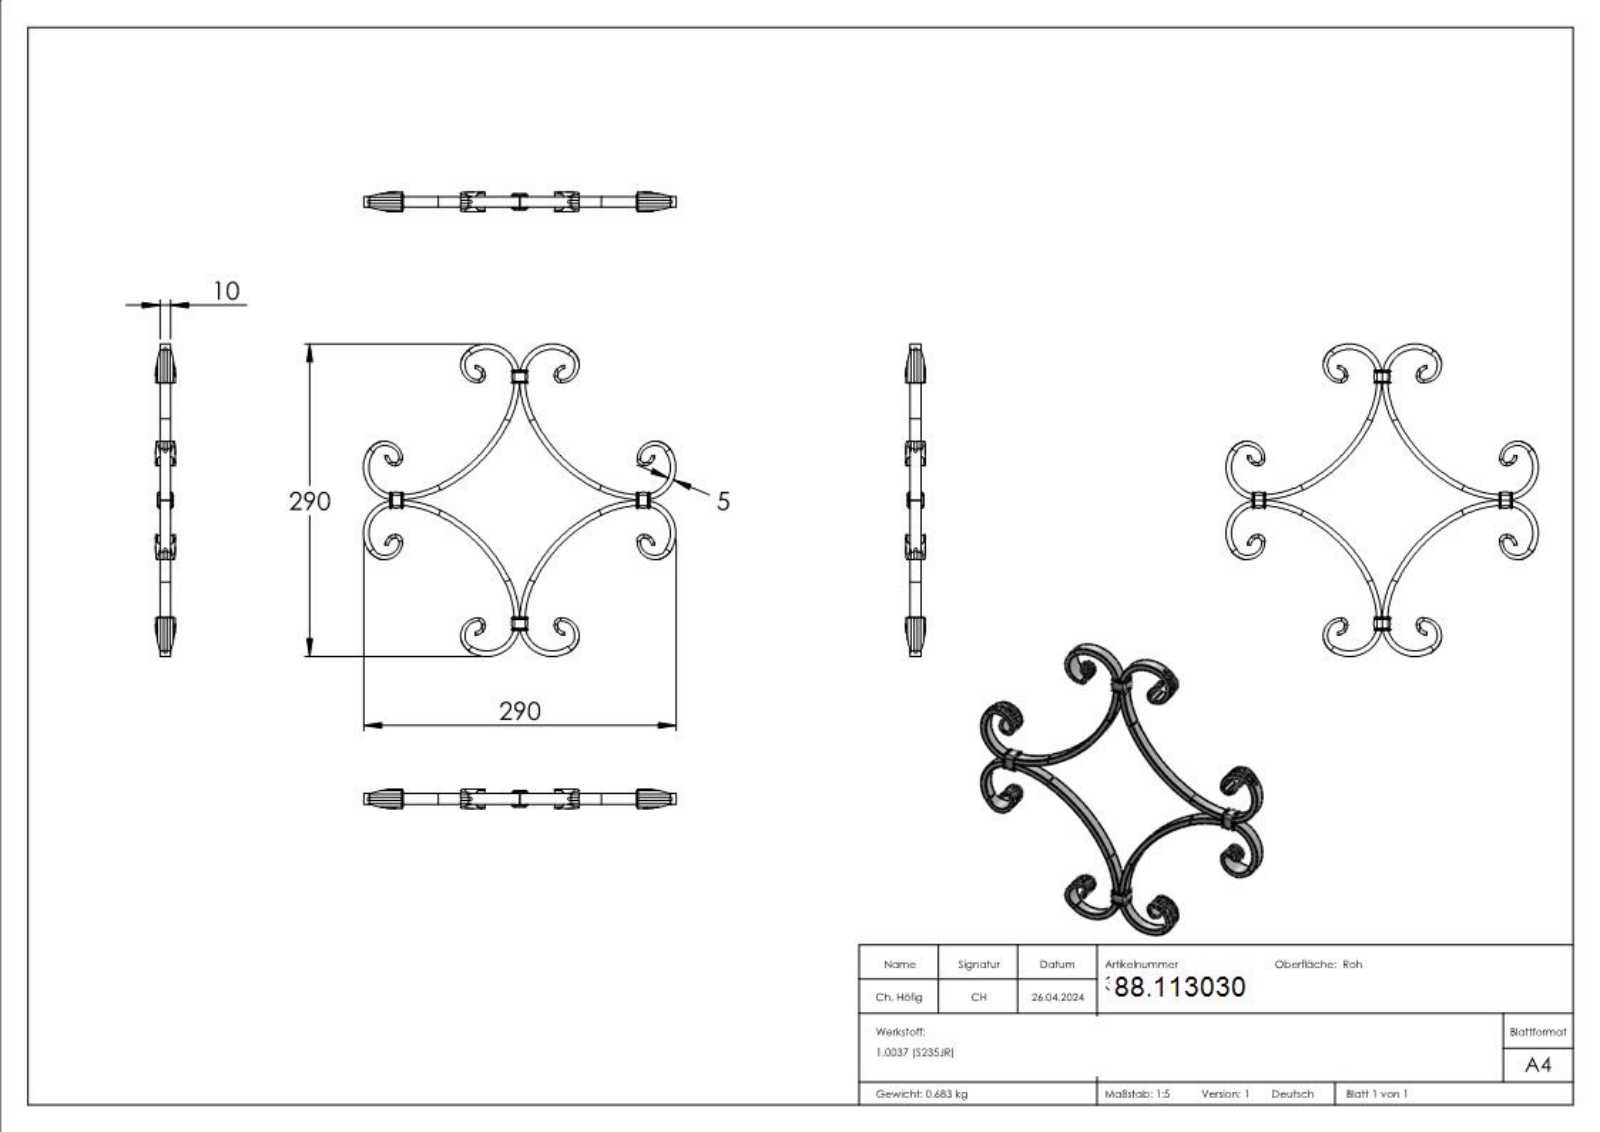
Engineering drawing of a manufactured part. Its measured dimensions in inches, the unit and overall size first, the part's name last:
Units: inches
Overall size (bounding box): 11.417 × 11.417 × 0.711
Partial cylindrical surfaces — rounded edges, fillets, slot ends (radius × count): R0.02 ×96, R0.004 ×32, R0.276 ×24, R0.098 ×8, R0.126 ×8, R0.244 ×8, R0.295 ×8, R0.394 ×8
Main face-to-face distances: 0.394, 0.157, 0.551, 9.018, 0.059, 0.413, 4.076, 4.47, 0.472, 4.548
Volume: 5.348 in³ · Surface area: 93.25 in²
Bodies: 8 solids, 1099 faces (361 planar, 348 cylindrical, 390 other)
Part name (STEP PRODUCT): 3030
STEP written by: SolidWorks 2018 (CONFIG_CONTROL_DESIGN)
